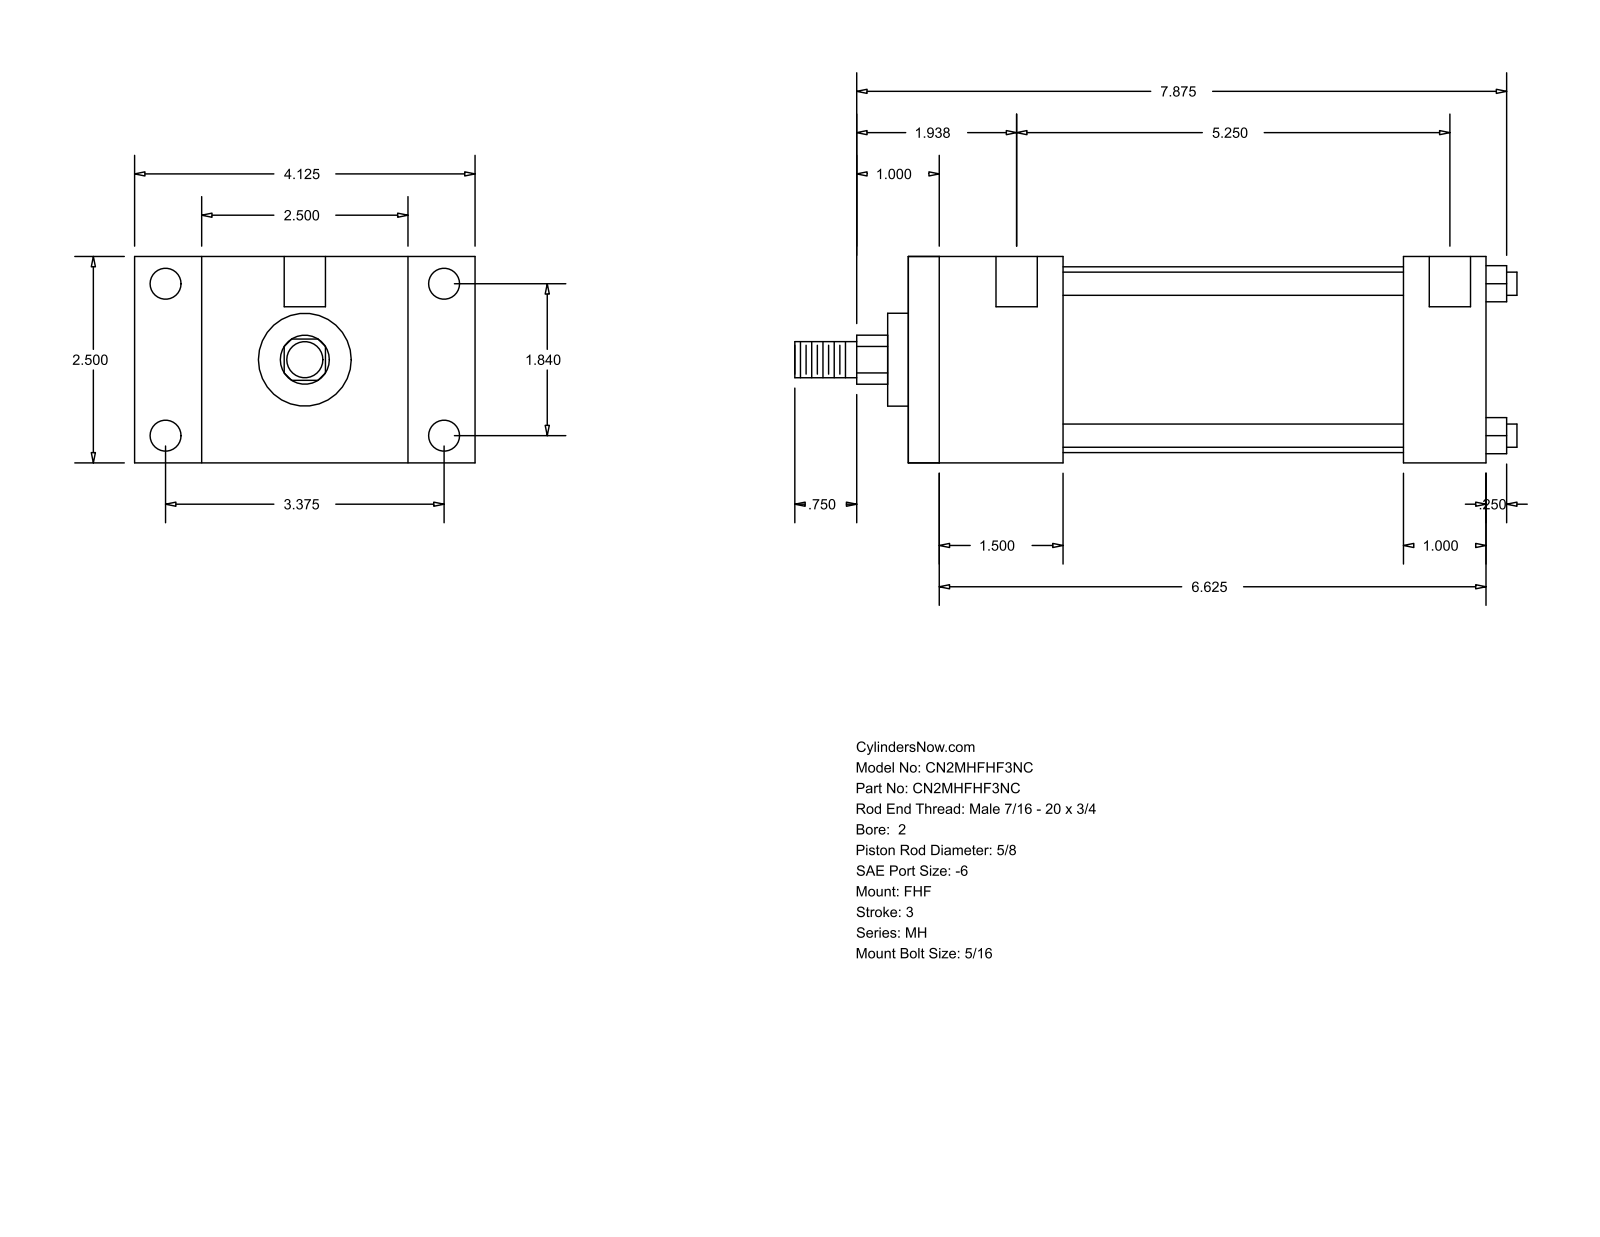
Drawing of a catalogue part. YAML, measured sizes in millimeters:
part_name: "MH_FHF__0200_0.625"
step_written_by: "GSSL Pune (CONFIG_CONTROL_DESIGN)"
units: millimeters
bodies: {solids: 0, faces: 88, planar: 60, cylindrical: 28, other: 0}
overall_size: [222.25, 104.78, 63.5]
round_holes:
  - {diameter: 5.56, count: 4}
  - {diameter: 9.53, count: 4}
  - {diameter: 12.7, count: 2}
round_bosses_or_shafts:
  - {diameter: 7.14, count: 4}
  - {diameter: 57.15, count: 1}
  - {diameter: 28.57, count: 1}
  - {diameter: 15.88, count: 1}
  - {diameter: 11.11, count: 1}
partial_cylinders:
  - {radius: 7.54, count: 1}
face_to_face_distances: [63.5, 104.78, 47.62, 177.8, 130.18, 20.64, 84.14, 25.4, 152.4, 6.35]
hole_center_spacings: [46.74, 85.72, 97.63, 141.29, 3.18, 4.76, 133.35, 136.53]
